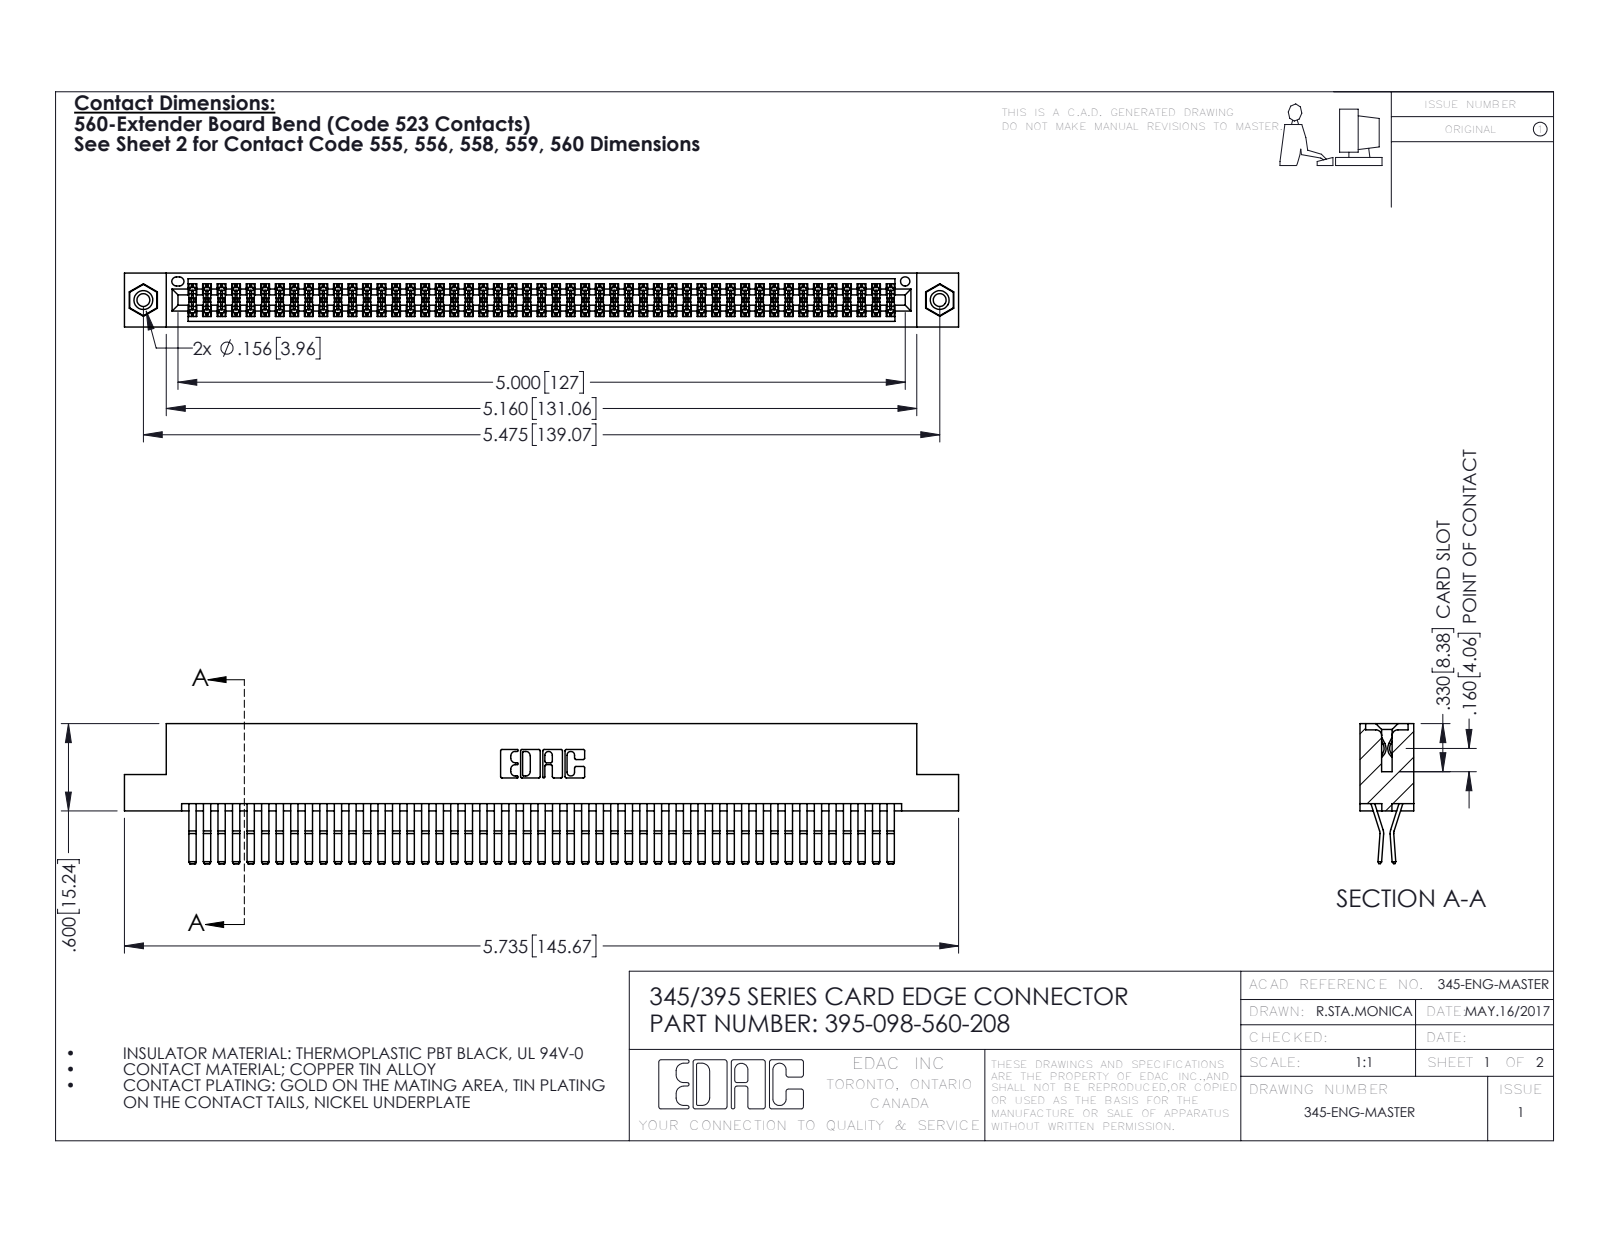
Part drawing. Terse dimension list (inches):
name: 345-292-001_560 Tail; 345 Part_Flush Mounting Lugs - 0.156 Dia-TI; 345-250-001_345-250-003-102; 395-098-560-208
written by: SolidWorks 2016 (CONFIG_CONTROL_DESIGN)
unit: in
bodies: 101 solids, 5282 faces (3346 planar, 1920 cylindrical, 16 other)
size: 5.735 × 0.962 × 0.37
volume: 0.906 in³; area: 36.82 in²
holes: 2× ⌀0.089, 2× ⌀0.125, 2× ⌀0.156, 1× ⌀0.064
bosses: 2× ⌀0.155
rounds: 147× R0.006, 22× R0.01, 6× R0.007, 6× R0.031, 3× R0.026, 2× R0.01, 2× R0.014, 2× R0.019
face distances: 0.025, 0.072, 0.298, 0.2, 0.37, 0.098, 0.272, 0.225, 0.175, 0.149
hole spacings: 0.27, 5.239, 5.475
